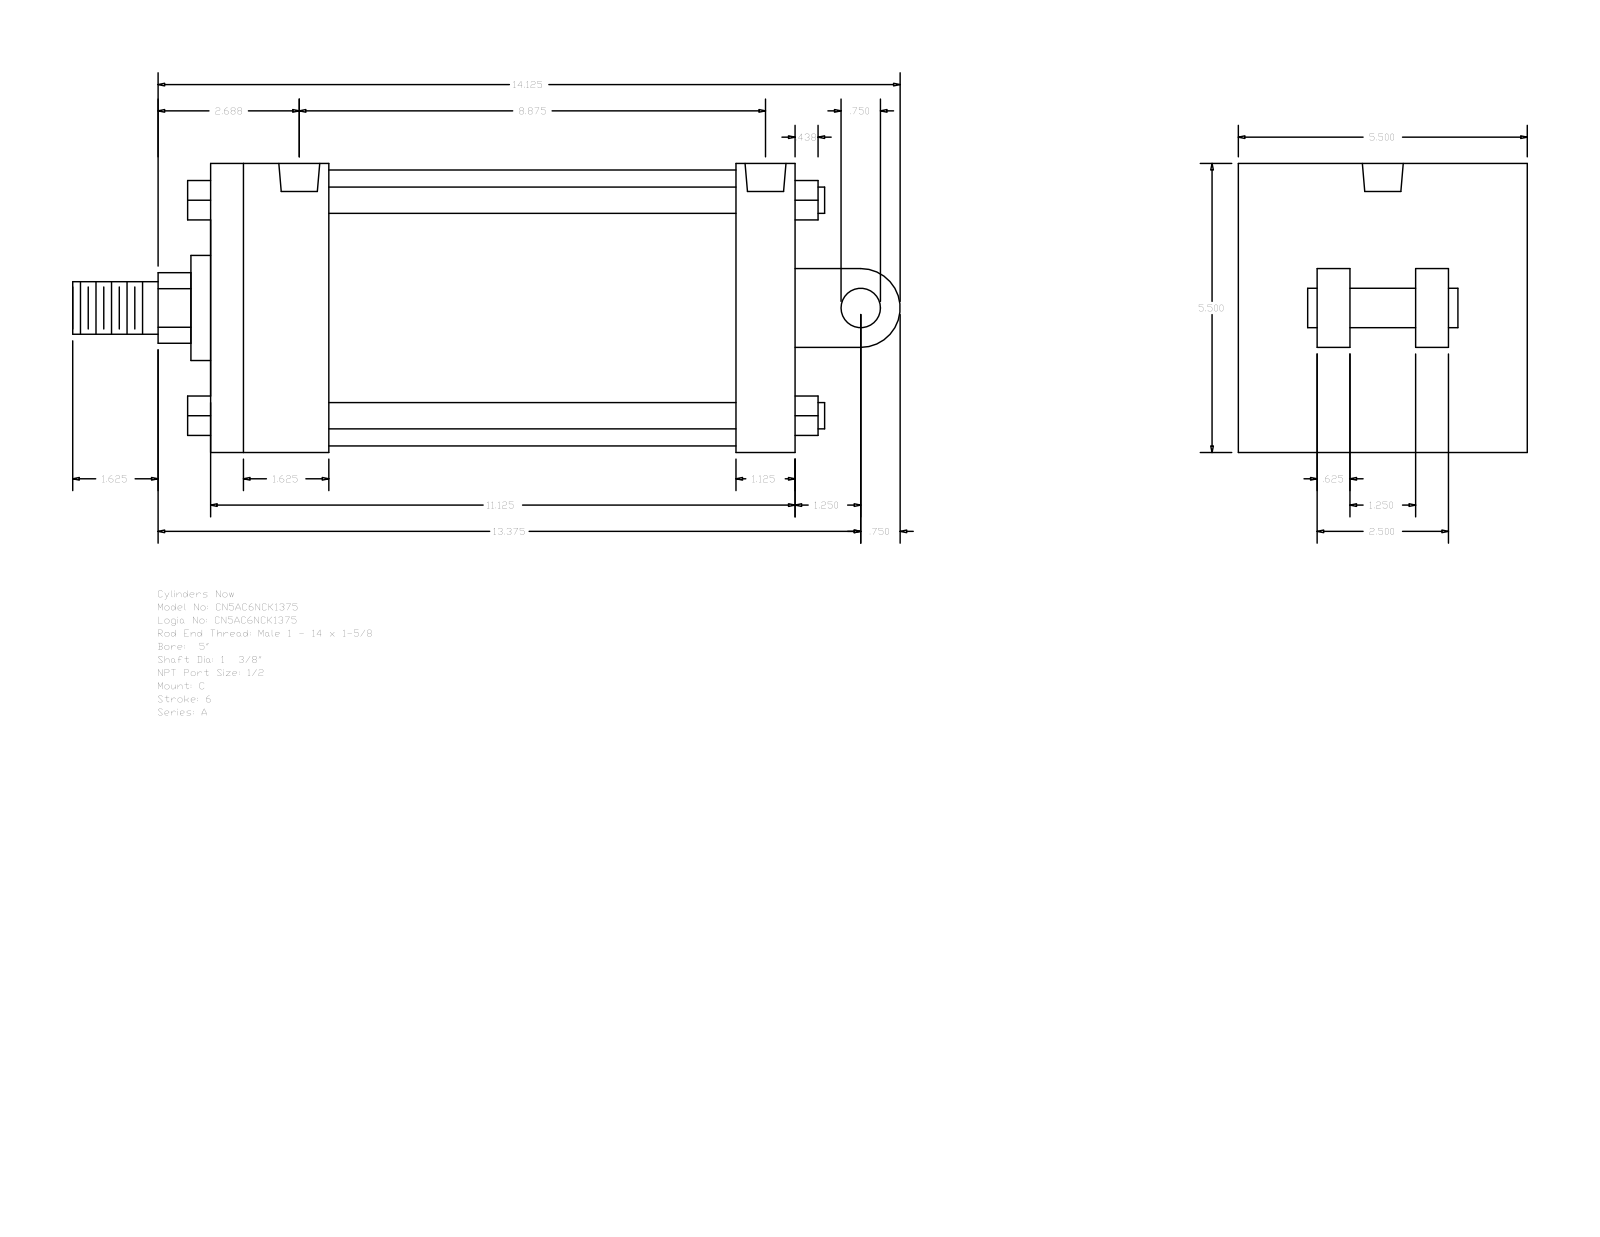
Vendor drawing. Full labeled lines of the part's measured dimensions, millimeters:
Part name (STEP PRODUCT): A_C__0500_1.375
STEP written by: GSSL Pune (CONFIG_CONTROL_DESIGN)
Units: millimetres
Bodies: 0 solids, 135 faces (102 planar, 33 cylindrical, 0 other)
Overall size (bounding box): 400.05 × 139.7 × 139.7
Round holes (diameter × count): ⌀8.73 ×4, ⌀19.77 ×2
Round bosses / shafts (diameter × count): ⌀12.7 ×4, ⌀133.35 ×1, ⌀50.8 ×1, ⌀34.92 ×1, ⌀25.4 ×1, ⌀19.05 ×1
Partial cylindrical surfaces — rounded edges, fillets, slot ends (radius × count): R17.06 ×1, R19.05 ×1
Main face-to-face distances: 139.7, 282.58, 57.15, 28.58, 254, 196.85, 225.43, 38.1, 53.97, 101.6
Hole centre spacings: 2.39, 220.65, 223.04, 225.43
